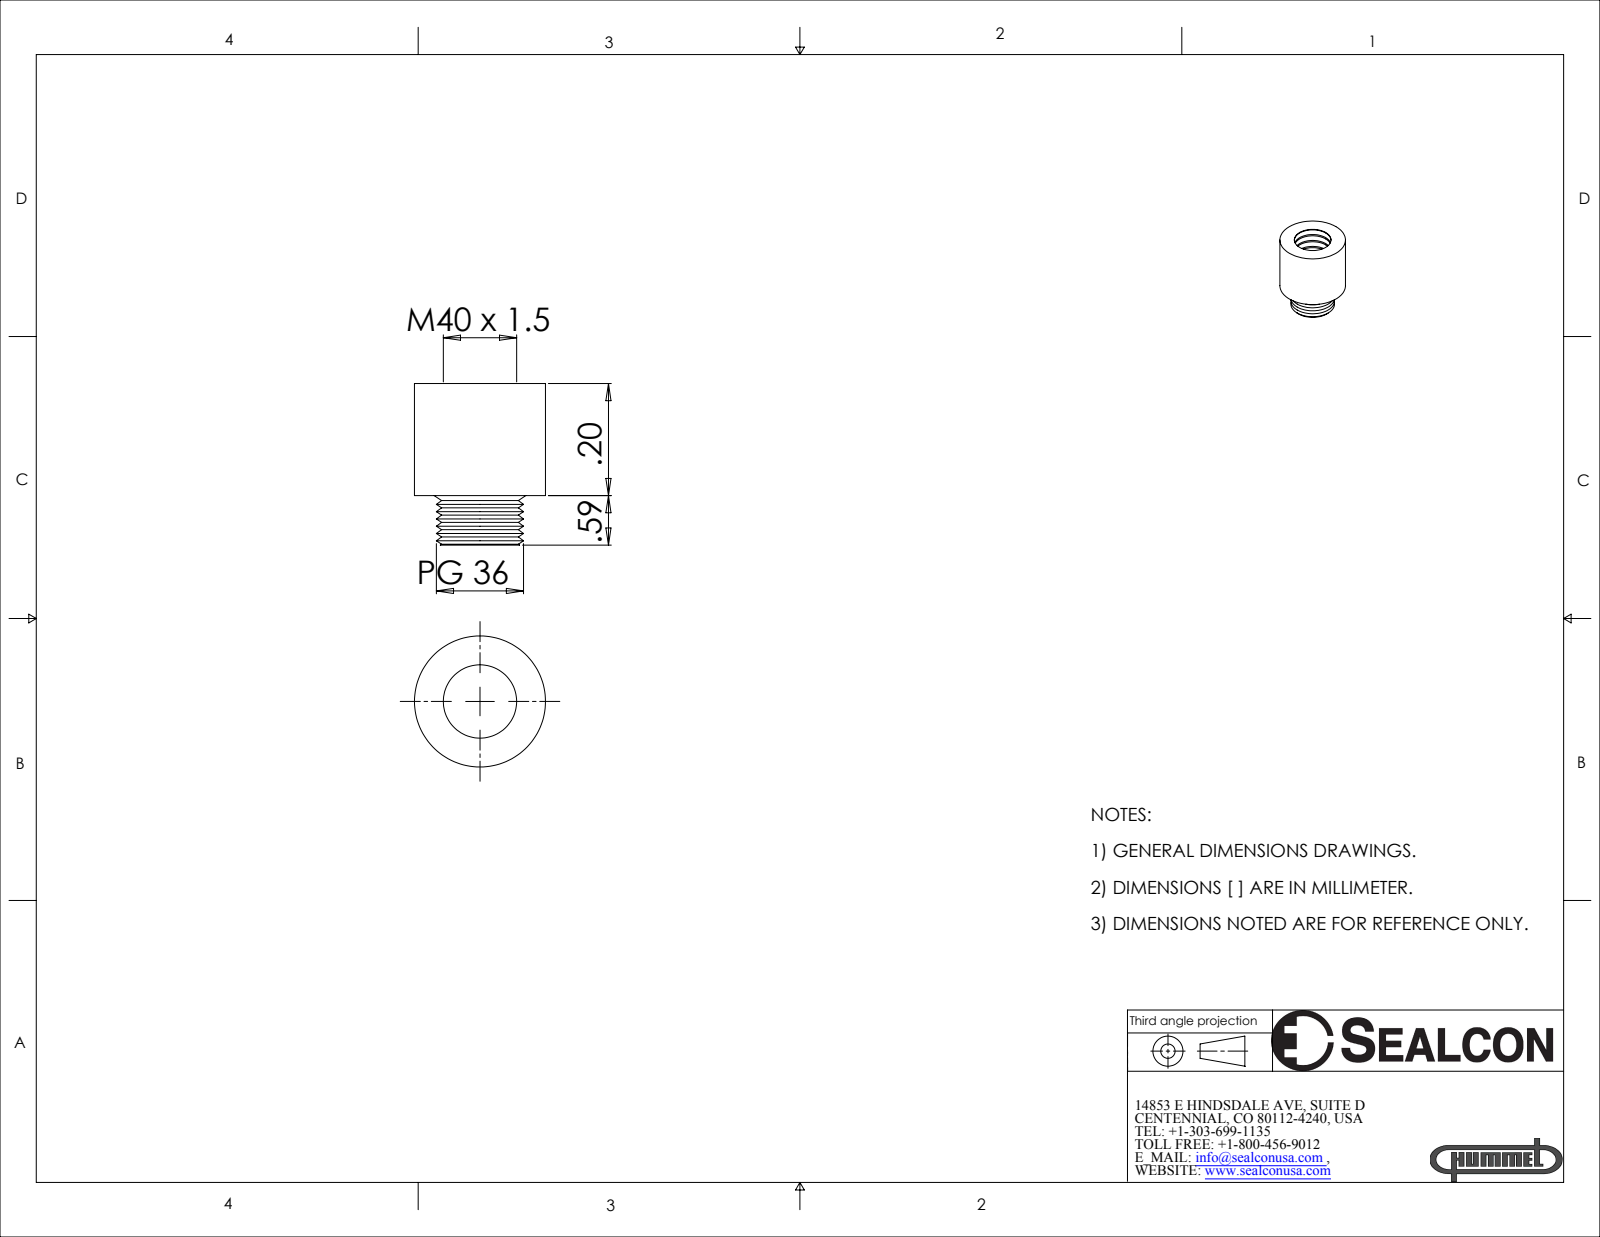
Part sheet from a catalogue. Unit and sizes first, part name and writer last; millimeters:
Units: millimetres
Overall size (bounding box): 28.2 × 22.9 × 22.9
Round holes (diameter × count): ⌀12.8 ×1
Round bosses / shafts (diameter × count): ⌀22.9 ×1
Main face-to-face distances: 19.6, 8.6, 28.2
Volume: 5 370 mm³ · Surface area: 4 259 mm²
Bodies: 1 solid, 77 faces (3 planar, 18 cylindrical, 56 other)
Part name (STEP PRODUCT): AP-3640-BK
STEP written by: SolidWorks 2008 (CONFIG_CONTROL_DESIGN)
